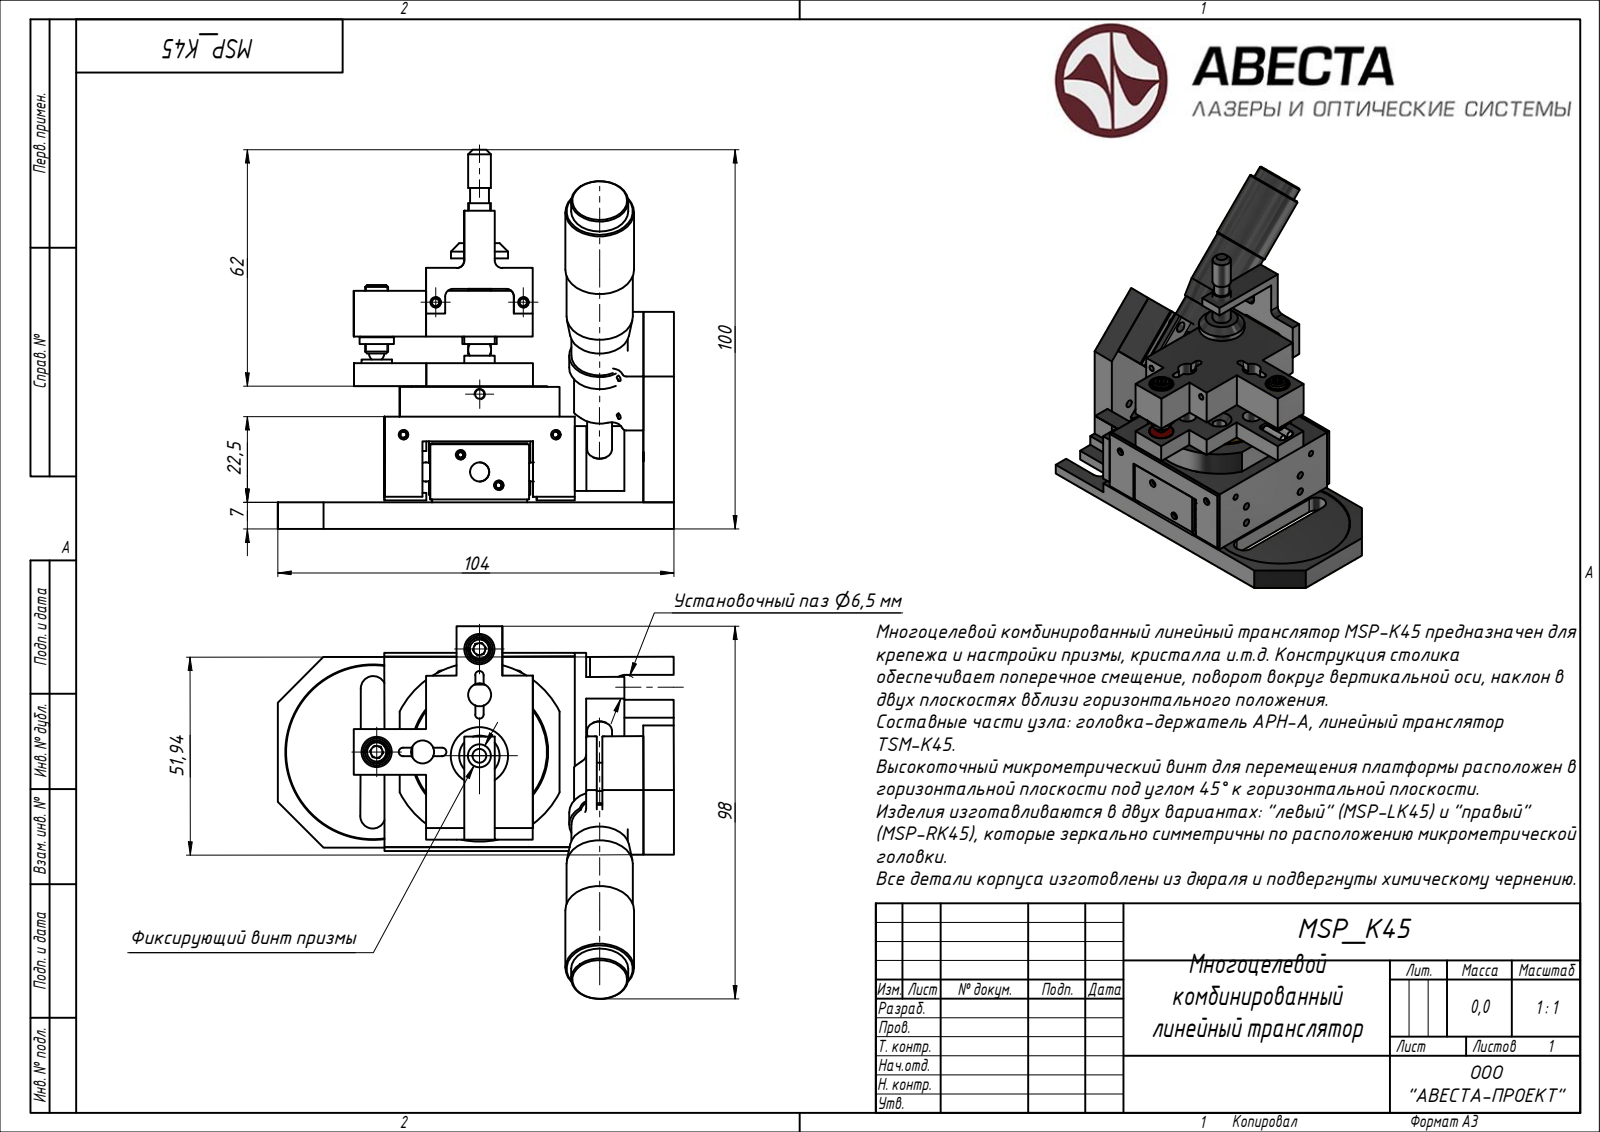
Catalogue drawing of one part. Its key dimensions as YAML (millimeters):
part_name: "Block 03; Block 02; Block 01"
step_written_by: "ST-DEVELOPER v15 (AUTOMOTIVE_DESIGN)"
units: millimeters
bodies: {solids: 25, faces: 1204, planar: 0, cylindrical: 0, other: 1204}
overall_size: [107.03, 99.52, 97.81]
